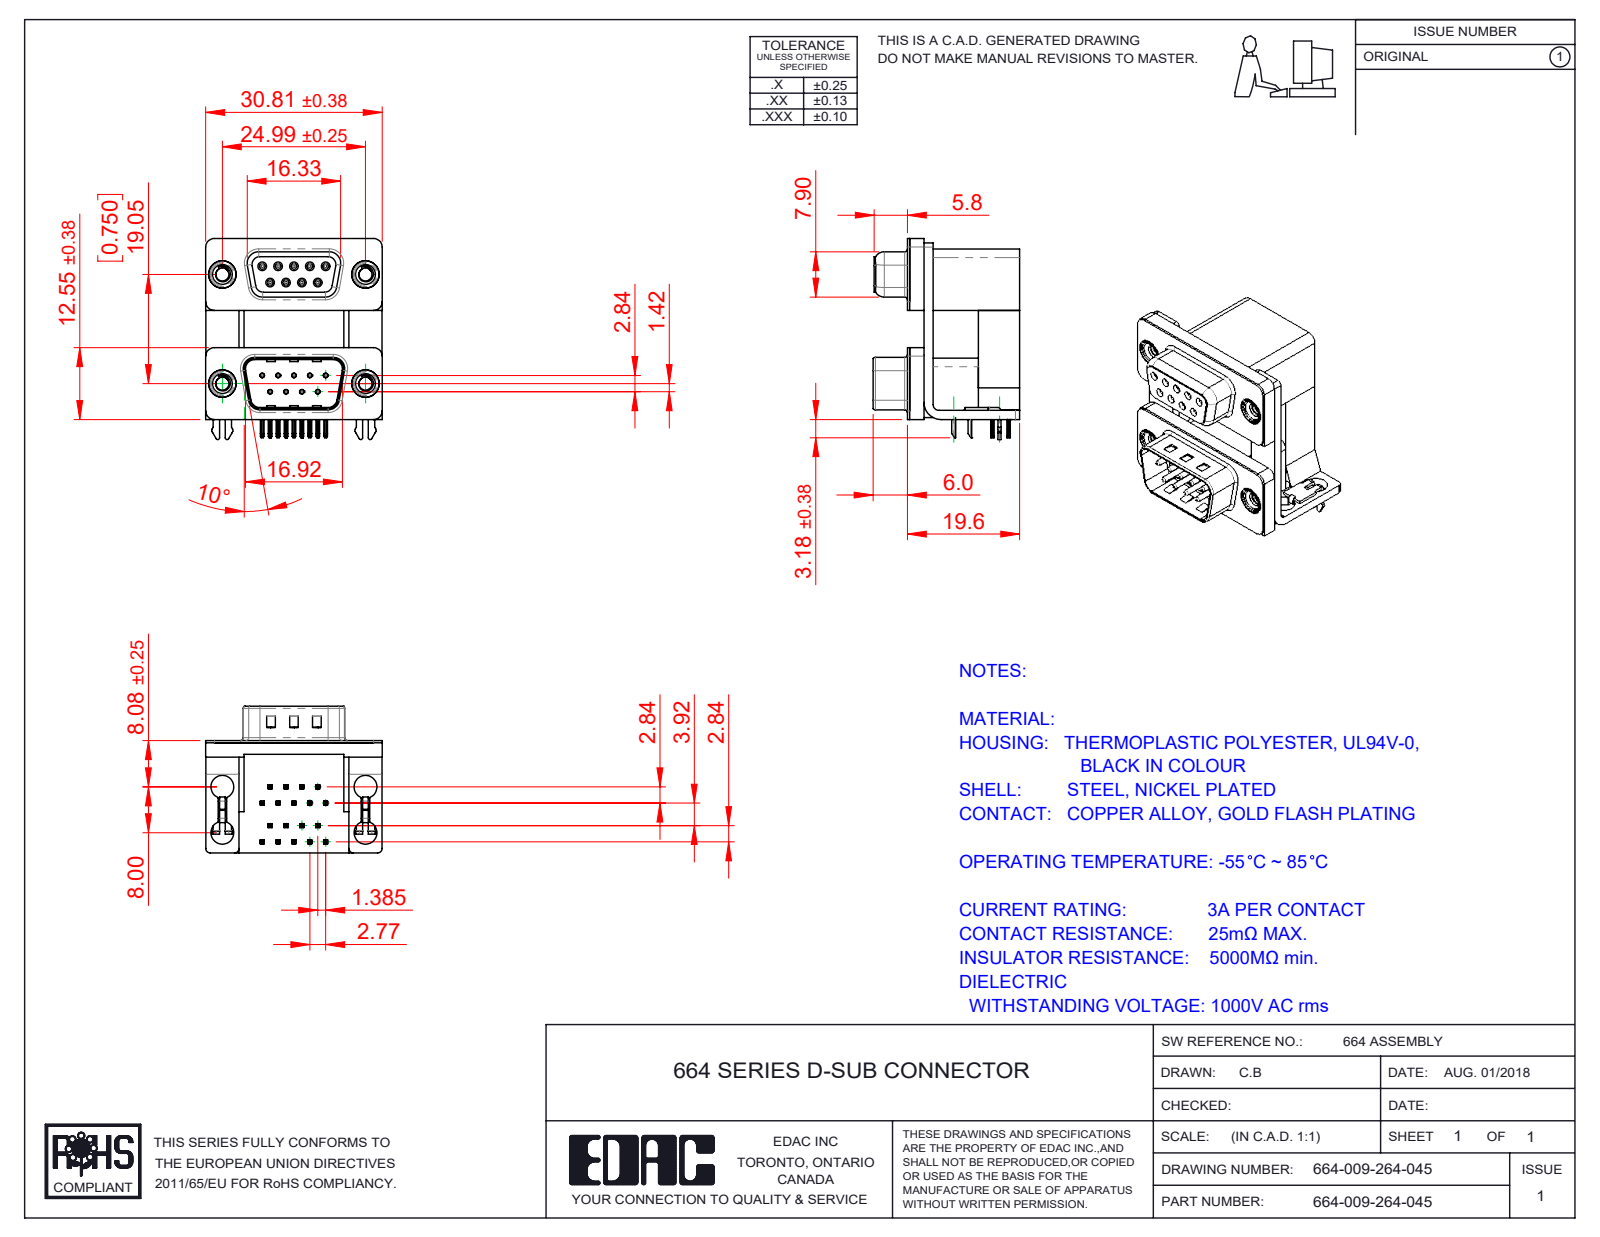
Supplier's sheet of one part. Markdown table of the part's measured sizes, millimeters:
| quantity | value |
| --- | --- |
| part name | 664 Shell Plug_09 Contacts; 664 Contact Top Upper_M; 664 Housing Spacer_09 Contacts M; 664 2 Prong Board Lock_4 (+8 more) |
| STEP written by | SolidWorks 2020 (CONFIG_CONTROL_DESIGN) |
| units | millimeters |
| bodies | 31 solids, 2637 faces (1341 planar, 725 cylindrical, 571 other) |
| overall size | 35.1 × 30.81 × 25.6 |
| volume | 10 767 mm³ |
| surface area | 12 708 mm² |
| round holes (diameter × count) | 0.8 × 18, 0.35 × 9, 0.9 × 9, 4 × 8, 2.26 × 4, 3.5 × 4, 4.8 × 4, 5 × 4 |
| round bosses / shafts (diameter × count) | 1.2 × 9, 0.75 × 9, 4.9 × 4, 4.75 × 4, 3.9 × 4 |
| partial cylindrical surfaces (radius × count) | 0.1 × 73, 0.25 × 42, 0.15 × 36, 0.12 × 18, 0.35 × 18, 0.5 × 16, 1.5 × 13, 0.75 × 10 |
| main face-to-face distances | 0.4, 2.5, 16.7, 19.2, 7.2, 9.5, 12, 1.6, 19.6, 12.4 |
| hole center spacings | 3.16, 2.77, 19.25, 19.05, 5.54, 19.84, 16.27, 21.93 |
